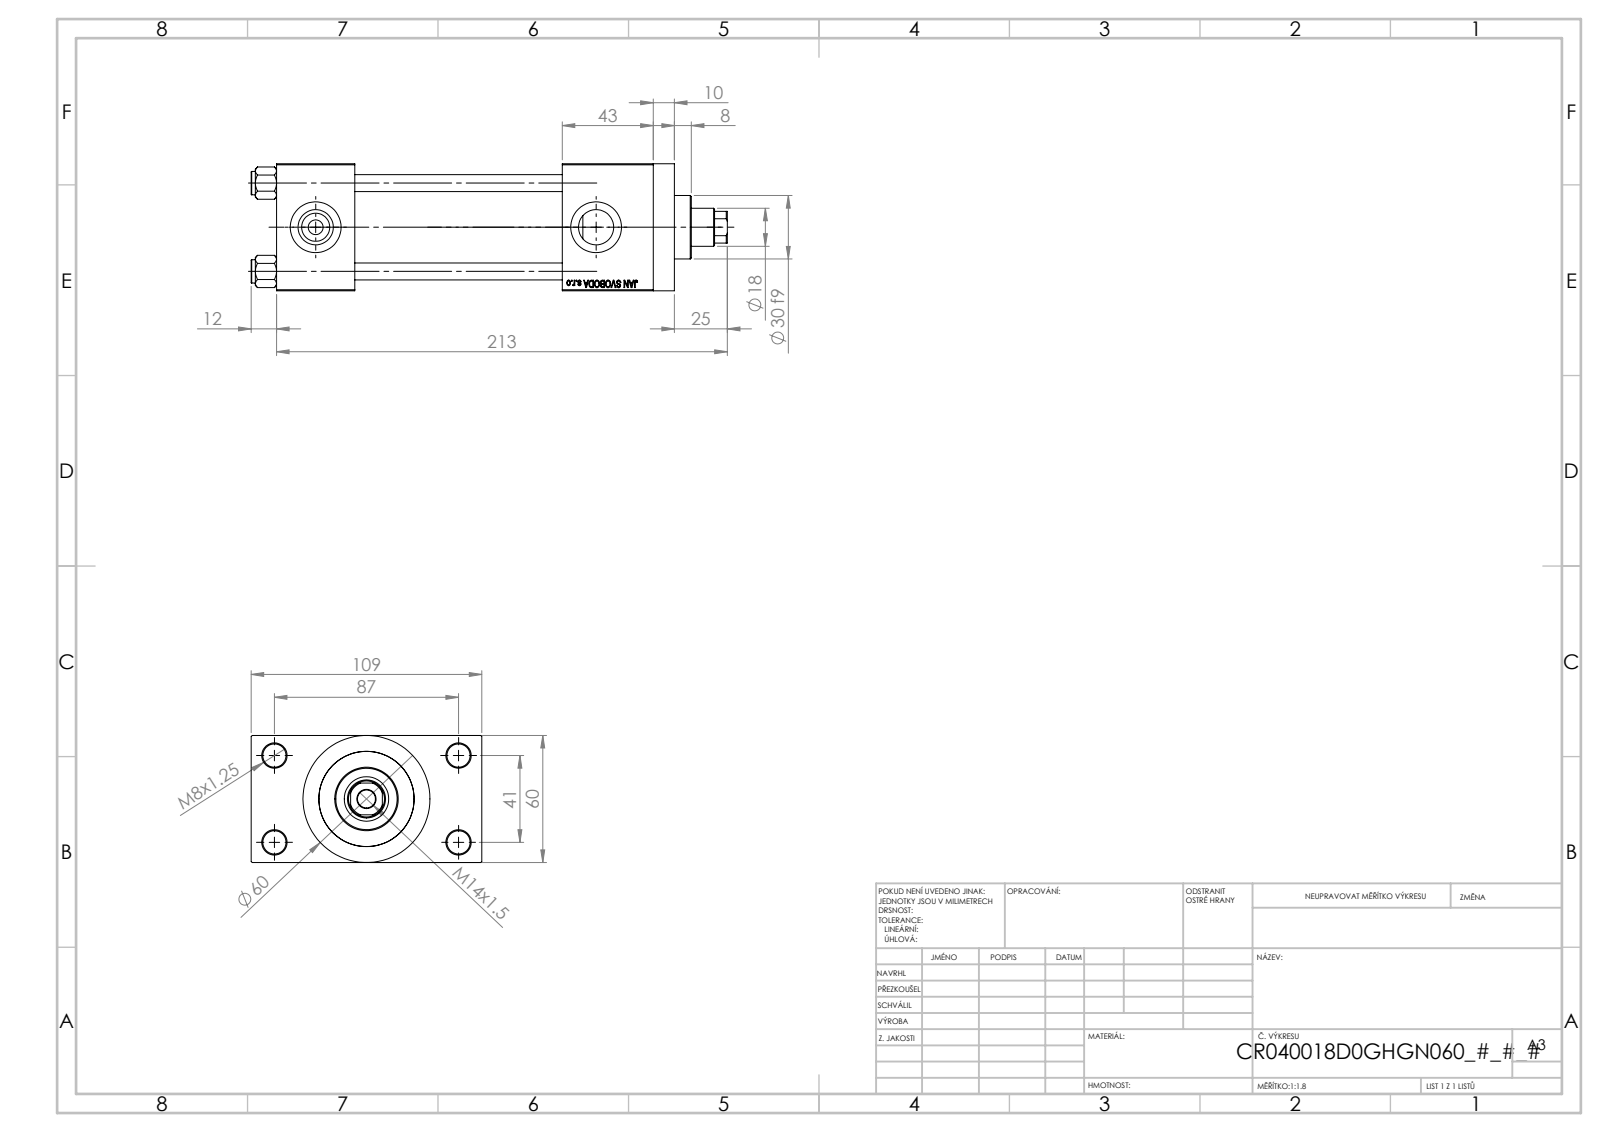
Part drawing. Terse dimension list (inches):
name: V215CR_D_Body; V215_VC_A; V215CR_D_TYCINKA; NUT_M5_D (+1 more)
written by: SolidWorks 2019 (CONFIG_CONTROL_DESIGN)
unit: in
bodies: 11 solids, 1104 faces (498 planar, 88 cylindrical, 518 other)
size: 8.858 × 4.291 × 2.362
volume: 33.38 in³; area: 216.4 in²
holes: 4× ⌀0.315, 4× ⌀0.433, 2× ⌀0.276, 2× ⌀0.656, 2× ⌀0.945, 1× ⌀0.335, 1× ⌀0.709, 1× ⌀0.827, 1× ⌀1.22, 1× ⌀1.575, 1× ⌀1.772
bosses: 4× ⌀0.433, 1× ⌀2.362, 1× ⌀1.811, 1× ⌀1.181
rounds: 1× R0.335
face distances: 2.362, 3.858, 0.965, 3.327, 1.457, 5.315, 7.008, 5.551, 1.693, 0.394
hole spacings: 0.892, 1.161, 1.642, 1.856, 1.893, 2.533, 3.011, 1.614
